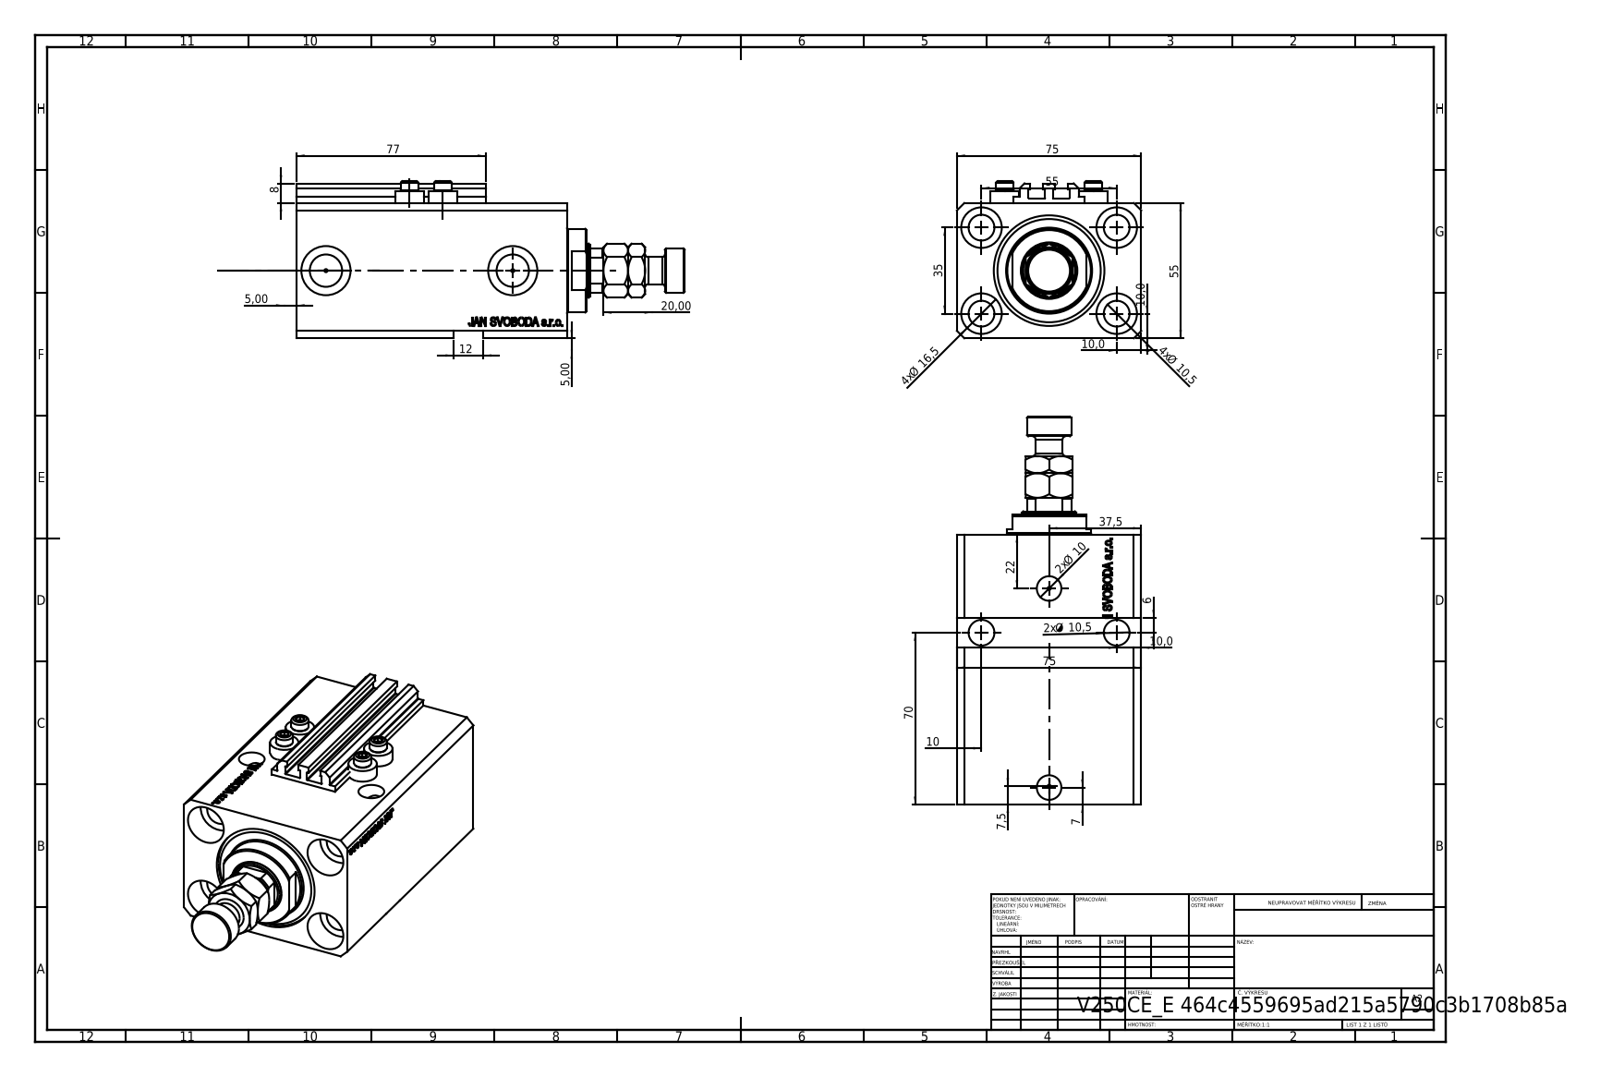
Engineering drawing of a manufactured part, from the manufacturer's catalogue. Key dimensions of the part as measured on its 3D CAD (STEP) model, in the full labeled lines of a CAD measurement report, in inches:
Part name (STEP PRODUCT): ALLEN BOLT V250CE; V250CE_C_VCP; V250CE_E_Body; MFA (+1 more)
STEP written by: SolidWorks 2019 (CONFIG_CONTROL_DESIGN)
Units: inches
Bodies: 9 solids, 1116 faces (530 planar, 130 cylindrical, 456 other)
Overall size (bounding box): 6.217 × 2.953 × 2.52
Volume: 24.15 in³ · Surface area: 154.1 in²
Round holes (diameter × count): ⌀0.413 ×7, ⌀0.049 ×4, ⌀0.157 ×4, ⌀0.65 ×4, ⌀0.394 ×2, ⌀0.518 ×2, ⌀0.787 ×2, ⌀0.866 ×1, ⌀1.26 ×1, ⌀1.772 ×1
Round bosses / shafts (diameter × count): ⌀0.457 ×4, ⌀0.276 ×4, ⌀1.339 ×1, ⌀0.709 ×1, ⌀0.433 ×1
Partial cylindrical surfaces — rounded edges, fillets, slot ends (radius × count): R0.008 ×10, R0.413 ×1
Main face-to-face distances: 2.165, 2.953, 4.331, 3.264, 1.067, 0.118, 0.39, 2.874, 3.941, 0.098
Hole centre spacings: 1.283, 2.165, 0.535, 0.555, 1.016, 1.294, 1.324, 1.378
